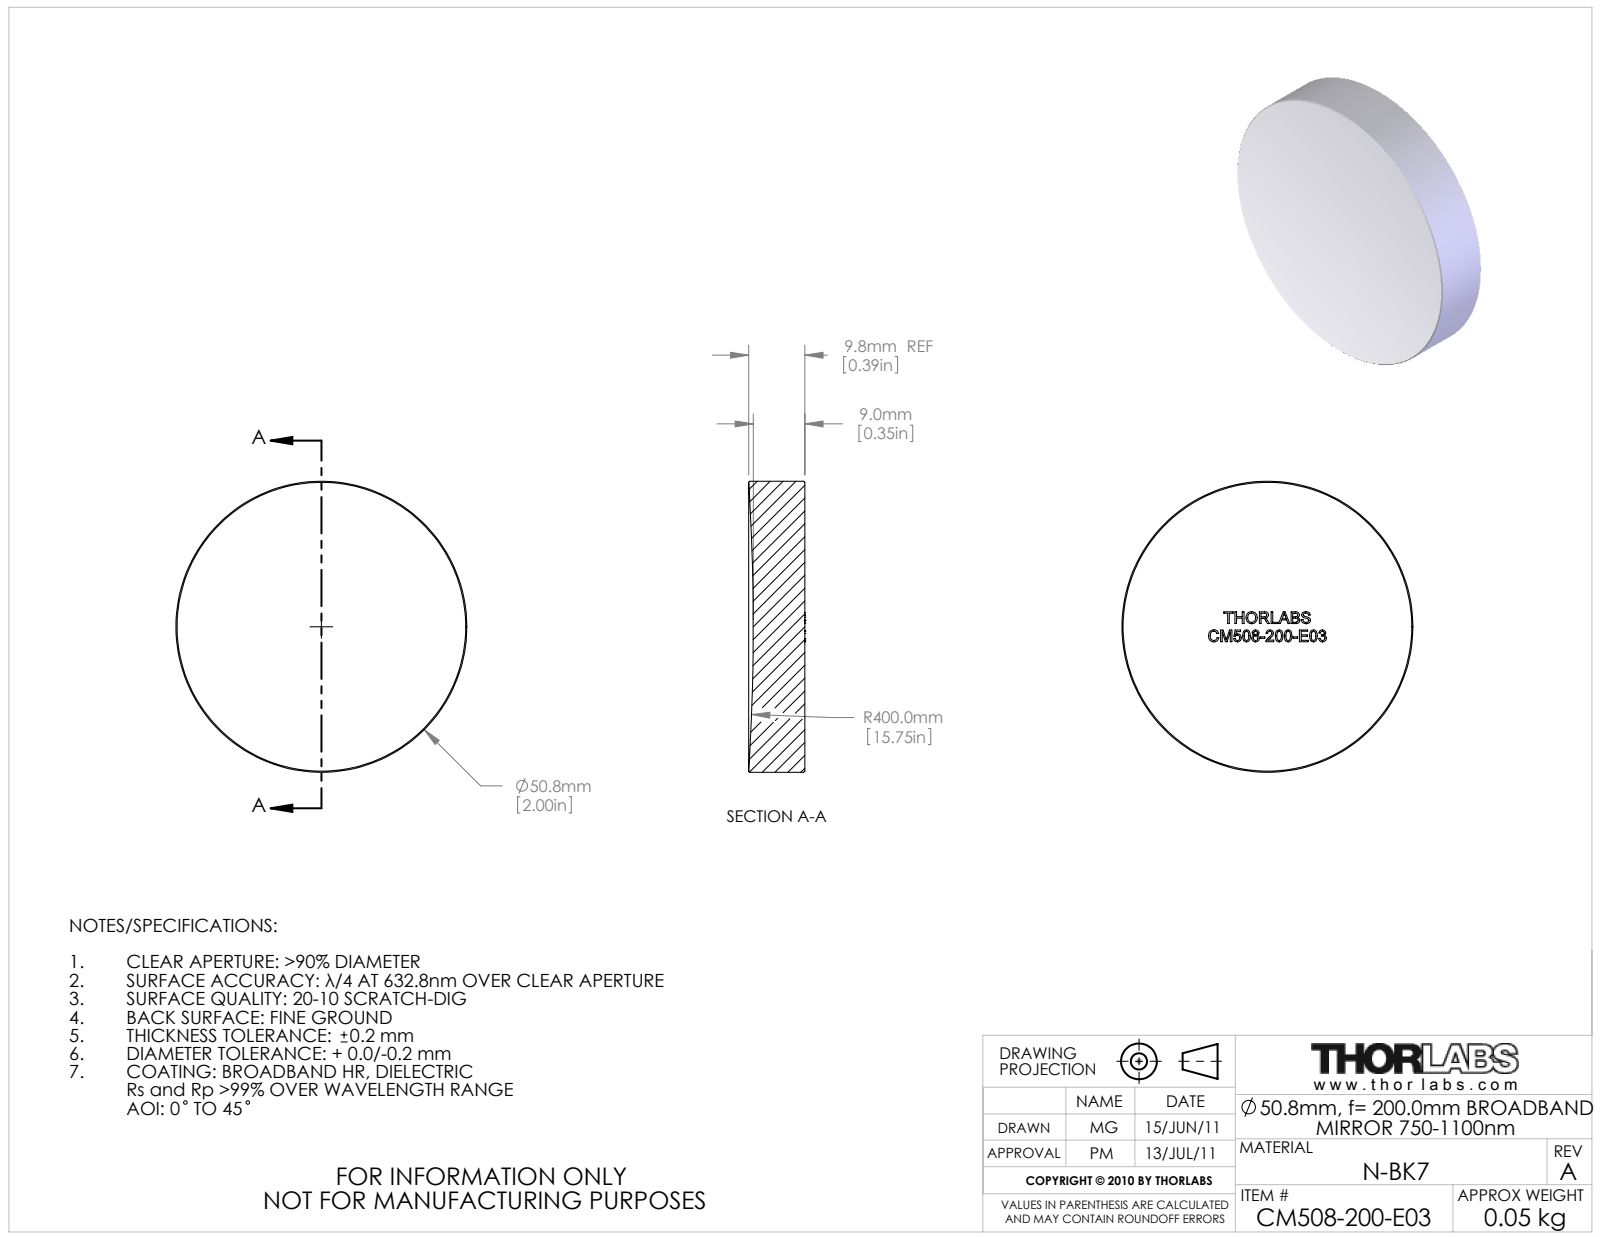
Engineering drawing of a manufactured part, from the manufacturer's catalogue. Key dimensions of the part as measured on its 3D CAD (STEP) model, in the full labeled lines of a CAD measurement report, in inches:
Part name (STEP PRODUCT): 22648-E0W
STEP written by: SolidWorks 2011 (AUTOMOTIVE_DESIGN)
Units: inches
Bodies: 0 solids, 43 faces (33 planar, 2 cylindrical, 8 other)
Overall size (bounding box): 2 × 2 × 0.385
Round bosses / shafts (diameter × count): ⌀2 ×1
